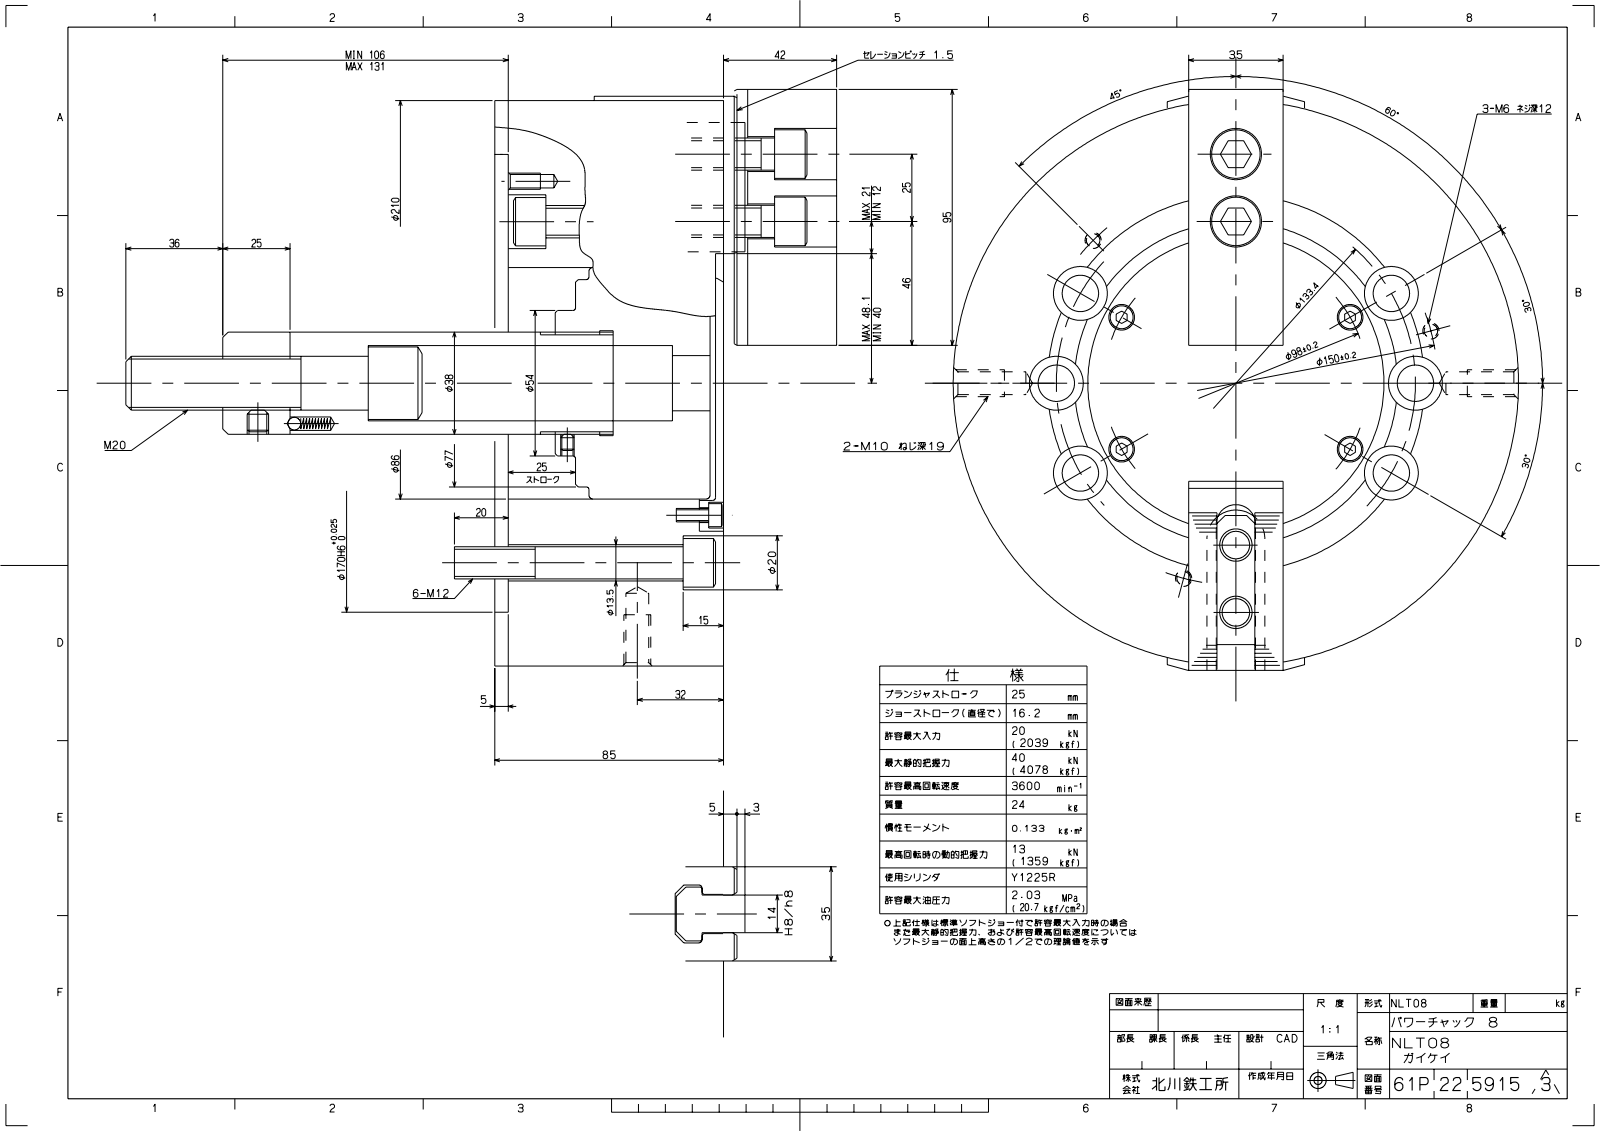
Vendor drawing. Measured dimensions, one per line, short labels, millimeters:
name: NLT08_mid stroke (2)
written by: ST-DEVELOPER v16.7 (AUTOMOTIVE_DESIGN)
unit: mm
bodies: 20 solids, 2319 faces (1600 planar, 562 cylindrical, 157 other)
size: 276.68 × 210 × 210
volume: 2 891 000 mm³; area: 389 548 mm²
holes: 9× ⌀20, 6× ⌀10.3, 6× ⌀13.5, 5× ⌀4.2, 4× ⌀4, 4× ⌀5.5, 4× ⌀9.5, 4× ⌀13, 4× ⌀19, 3× ⌀5.2, 2× ⌀14, 1× ⌀5
bosses: 6× ⌀18, 6× ⌀11.7, 1× ⌀210, 1× ⌀85, 1× ⌀54, 1× ⌀38, 1× ⌀30, 1× ⌀19.62
rounds: 10× R0.8, 4× R0.4, 4× R0.6, 4× R4.5, 2× R1.2, 2× R7.3, 2× R10.75, 1× R43.5
face distances: 6, 35, 80, 5, 33, 43, 85, 3, 24.5, 17.5
hole spacings: 66.7, 49, 75, 15, 17.69, 21.21, 34.48, 34.53
